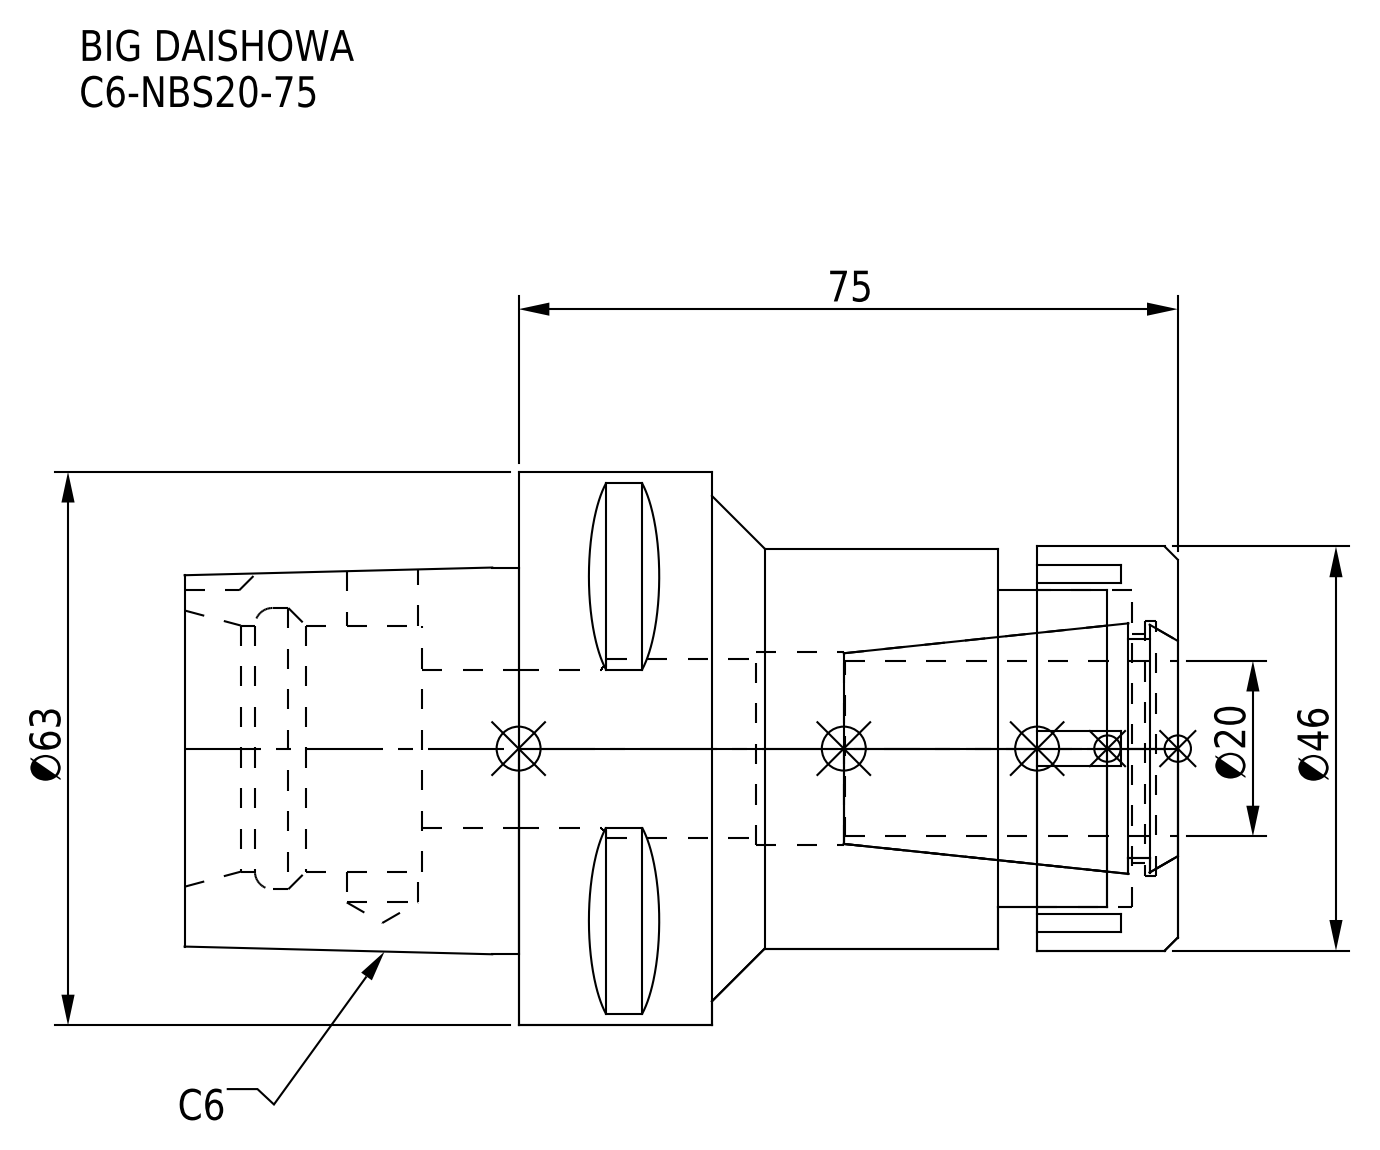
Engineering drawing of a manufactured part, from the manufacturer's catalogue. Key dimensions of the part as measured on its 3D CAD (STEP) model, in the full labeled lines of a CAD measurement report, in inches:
Part name (STEP PRODUCT): C6-NBS20-75; DXF_TEMP_ASSY_ASM_4_ASM.stp; NBN20_1.stp; C6-NBS20-75-FreeParts (+3 more)
STEP written by: SolidWorks 2019 (CONFIG_CONTROL_DESIGN)
Units: inches
Bodies: 2 solids, 112 faces (61 planar, 33 cylindrical, 18 other)
Overall size (bounding box): 4.449 × 2.48 × 2.48
Volume: 9.421 in³ · Surface area: 55.07 in²
Round holes (diameter × count): ⌀0.319 ×1, ⌀0.709 ×1, ⌀0.728 ×1, ⌀0.799 ×1, ⌀0.866 ×1, ⌀1.024 ×1, ⌀1.102 ×1, ⌀1.142 ×1, ⌀1.26 ×1, ⌀1.417 ×1
Round bosses / shafts (diameter × count): ⌀2.48 ×1, ⌀1.811 ×1, ⌀1.791 ×1
Partial cylindrical surfaces — rounded edges, fillets, slot ends (radius × count): R0.197 ×1
Main face-to-face distances: 2.953, 0.315, 0.807, 2.146, 2.323, 0.63, 0.177, 1.496, 0.866, 1.457
